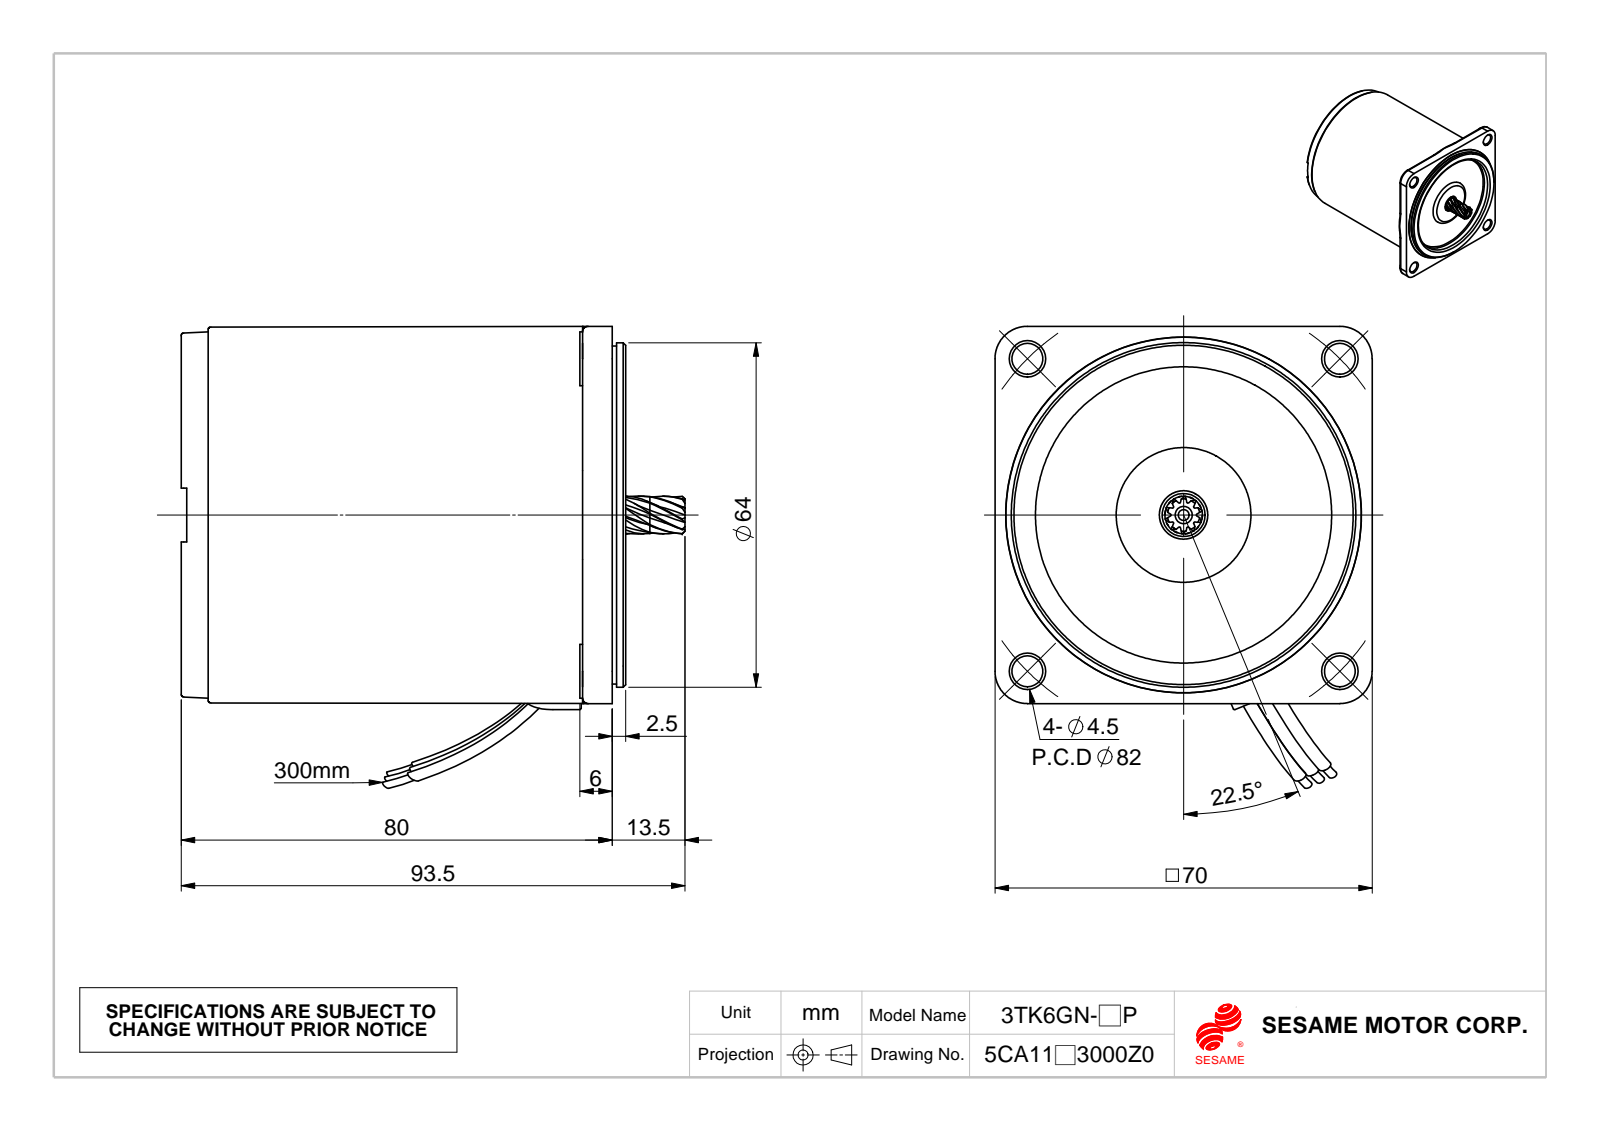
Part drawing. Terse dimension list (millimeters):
name: 線扣; 15GN_0.成品; M315_2車工; C364_車工(成品)
written by: SolidWorks 2010 (CONFIG_CONTROL_DESIGN)
unit: mm
bodies: 7 solids, 292 faces (72 planar, 82 cylindrical, 138 other)
size: 93.5 × 85.74 × 70
volume: 311 750 mm³; area: 39 193 mm²
holes: 4× ⌀5.75, 1× ⌀2, 1× ⌀7.2, 1× ⌀9, 1× ⌀9.5, 1× ⌀18, 1× ⌀55, 1× ⌀58.2, 1× ⌀60.5, 1× ⌀66
bosses: 4× ⌀10, 1× ⌀63.93, 1× ⌀62.73, 1× ⌀57.42, 1× ⌀57.2, 1× ⌀9.3, 1× ⌀8, 1× ⌀6.99
rounds: 8× R0.25, 4× R1, 4× R6, 1× R5.25, 1× R33.98
face distances: 77.4, 77.5, 1.51, 75.89, 1.61, 1.5, 79, 3.11, 1.6, 4
hole spacings: 41.01, 58, 82.02
